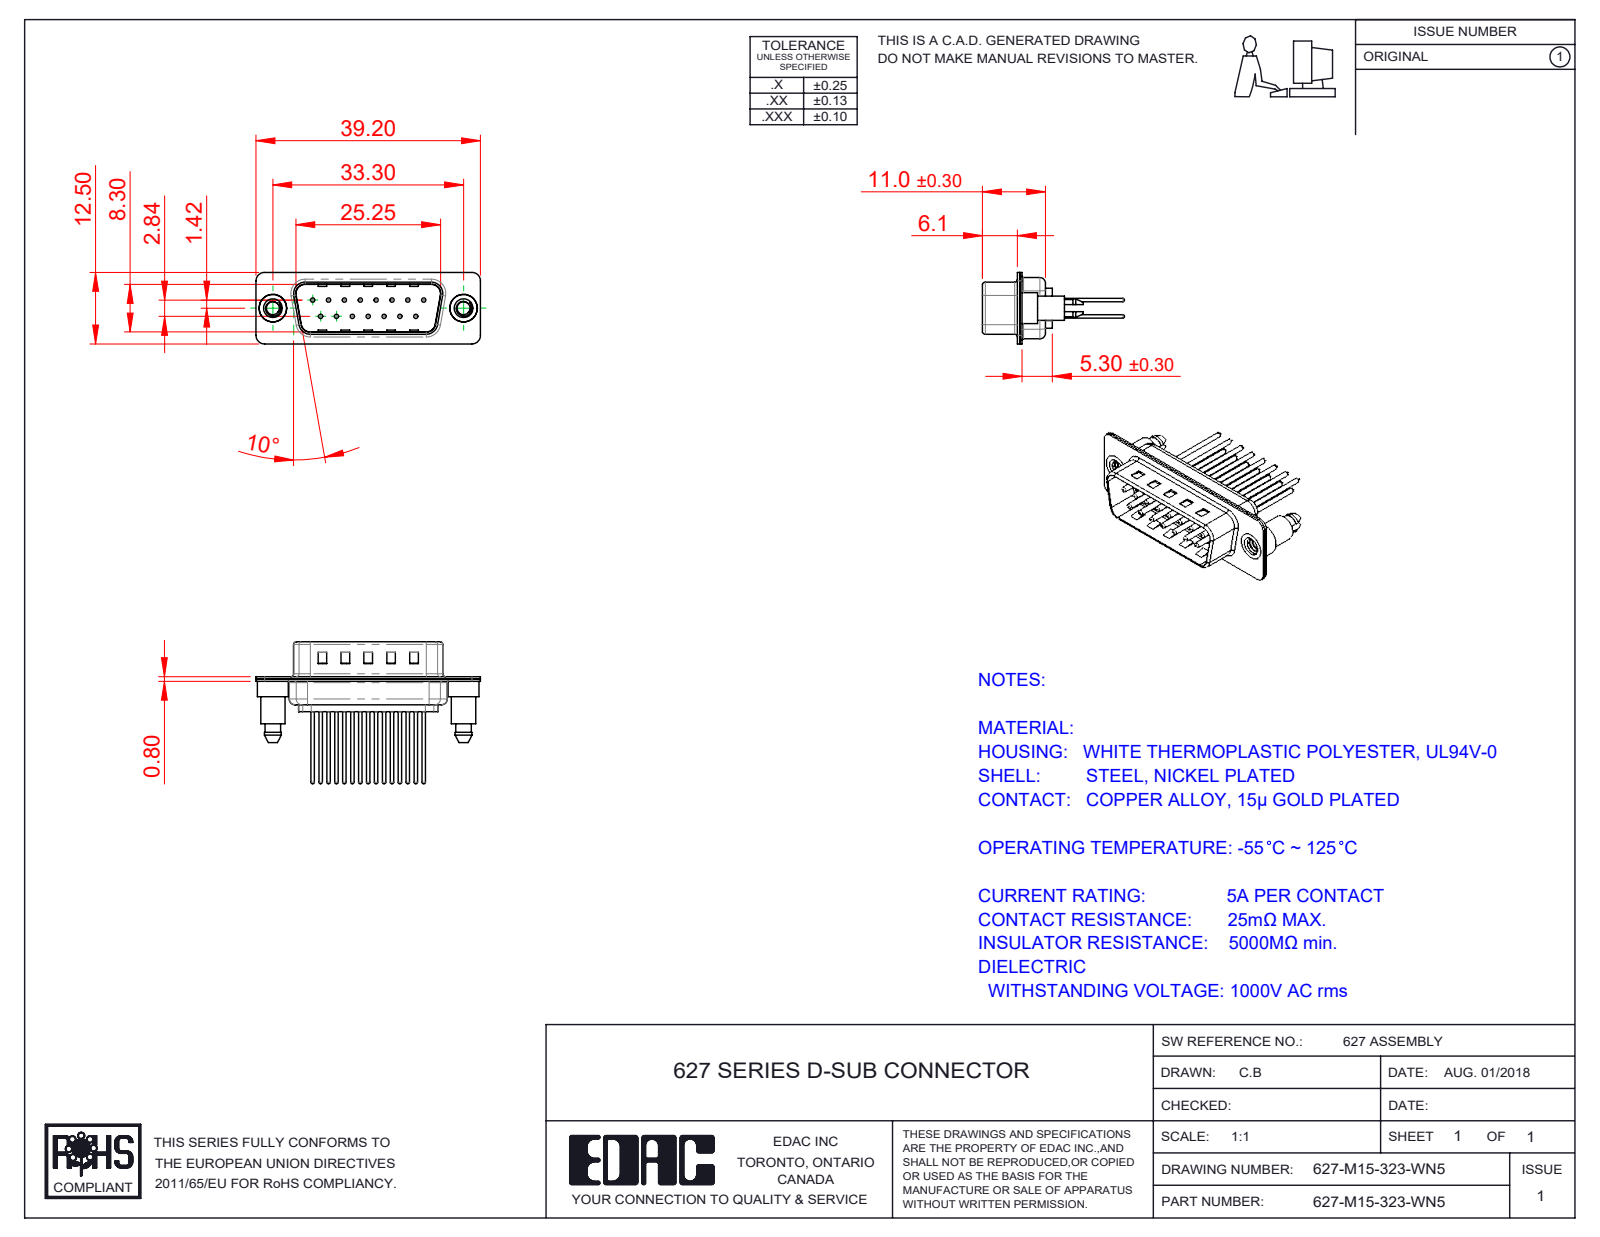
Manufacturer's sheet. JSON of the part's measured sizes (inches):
{"part_name": "627M Housing_15 Contacts; 627M 4-40 Threaded Boardlock; 627-M15-323-WN5; 627M Shell Front_15 Contacts (+3 more)", "step_written_by": "SolidWorks 2020 (CONFIG_CONTROL_DESIGN)", "units": "inches", "bodies": {"solids": 20, "faces": 945, "planar": 260, "cylindrical": 375, "other": 310}, "overall_size": [1.543, 0.975, 0.492], "volume_in3": 0.122, "surface_area_in2": 8.271, "round_holes": [[0.03, 15], [0.063, 15], [0.079, 15], [0.089, 2], [0.157, 2], [0.189, 2]], "round_bosses_or_shafts": [[0.059, 15], [0.024, 15], [0.213, 2], [0.193, 2], [0.167, 2]], "partial_cylinders_radius": [[0.059, 18], [0.079, 12], [0.063, 10], [0.02, 8], [0.01, 4], [0.024, 4], [0.026, 4], [0.035, 4]], "face_to_face_distances": [0.016, 0.031, 0.374, 0.358, 0.343, 0.39, 0.209, 0.047, 0.24, 0.224], "hole_center_spacings": [0.124, 0.109, 0.218, 0.327, 0.436, 0.198, 0.198, 0.294]}
